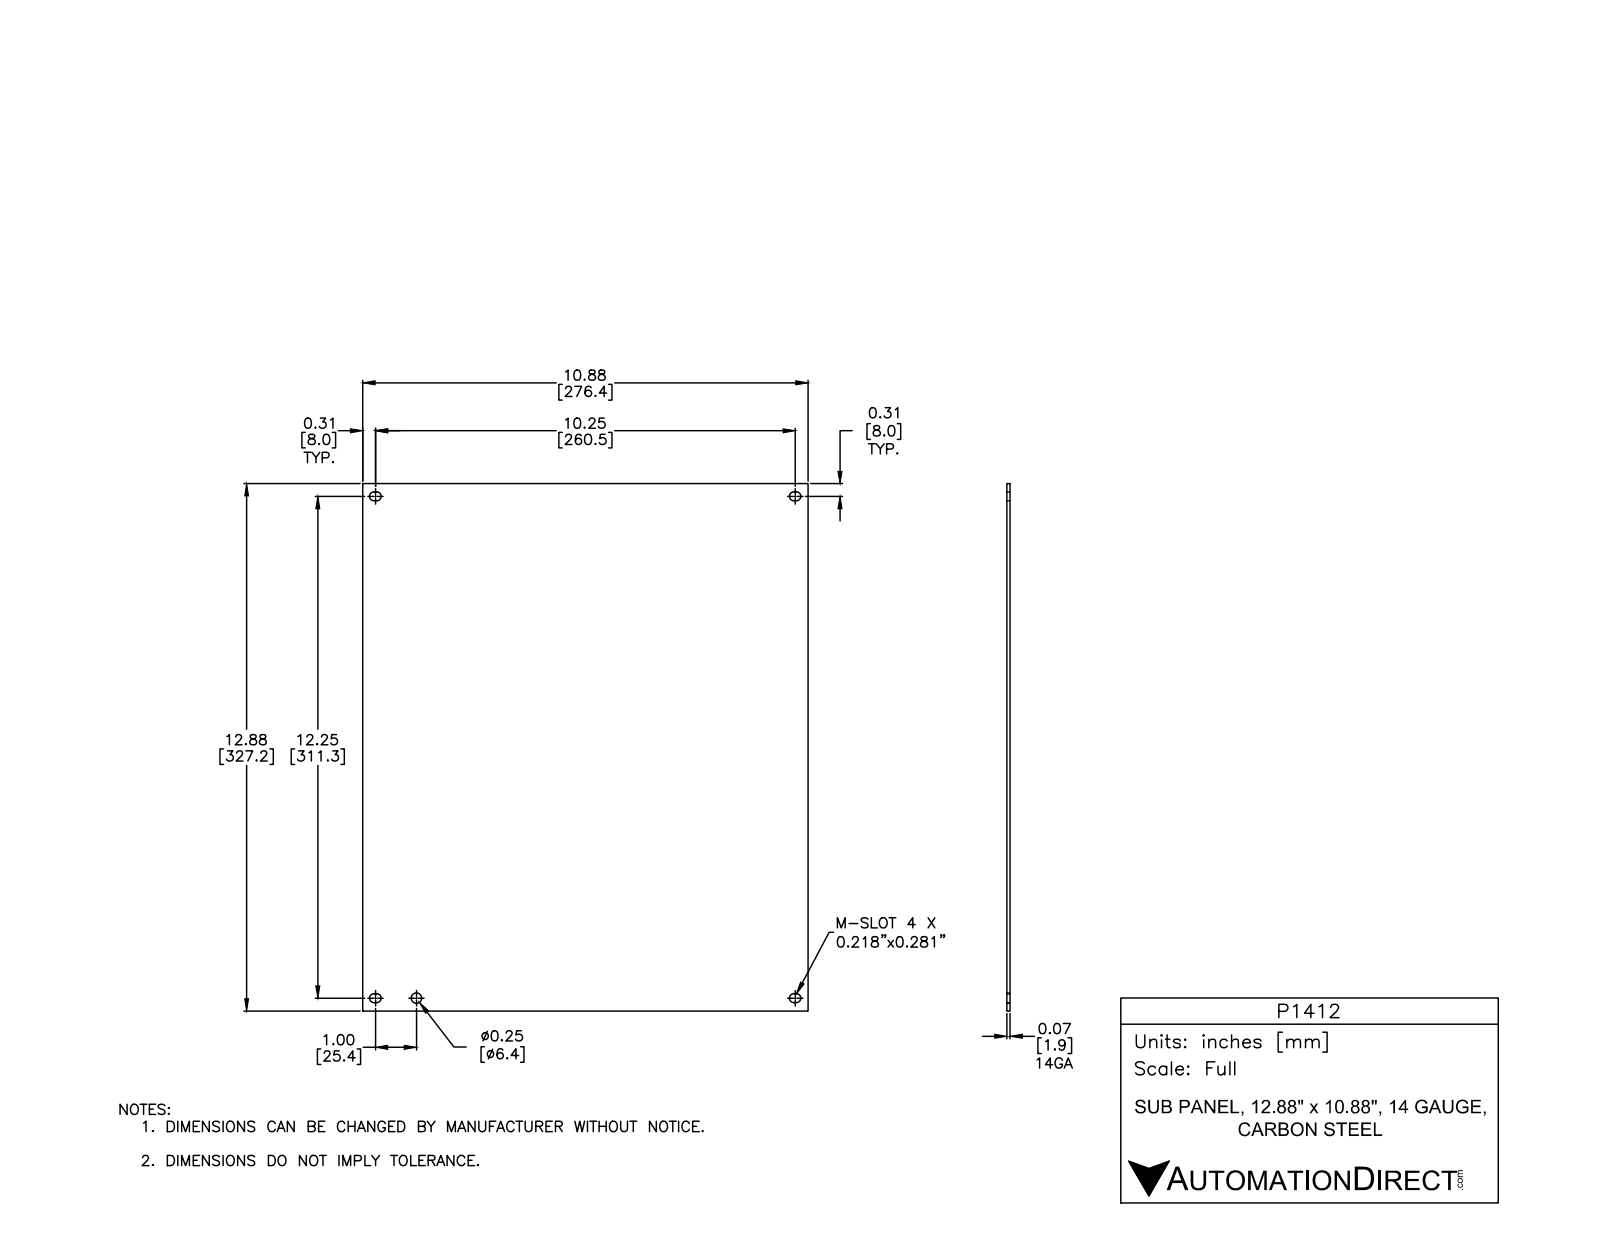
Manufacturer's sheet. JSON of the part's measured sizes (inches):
{"part_name": "P1412", "step_written_by": "Autodesk Inventor 2012 (AUTOMOTIVE_DESIGN)", "units": "inches", "bodies": {"solids": 1, "faces": 23, "planar": 14, "cylindrical": 9, "other": 0}, "overall_size": [12.88, 10.88, 0.074], "volume_in3": 10.35, "surface_area_in2": 283.6, "round_holes": [[0.25, 1]], "partial_cylinders_radius": [[0.109, 8]], "face_to_face_distances": [0.074, 10.88, 12.88, 0.422, 12.458, 0.204, 12.676, 0.218, 12.254, 12.472]}
